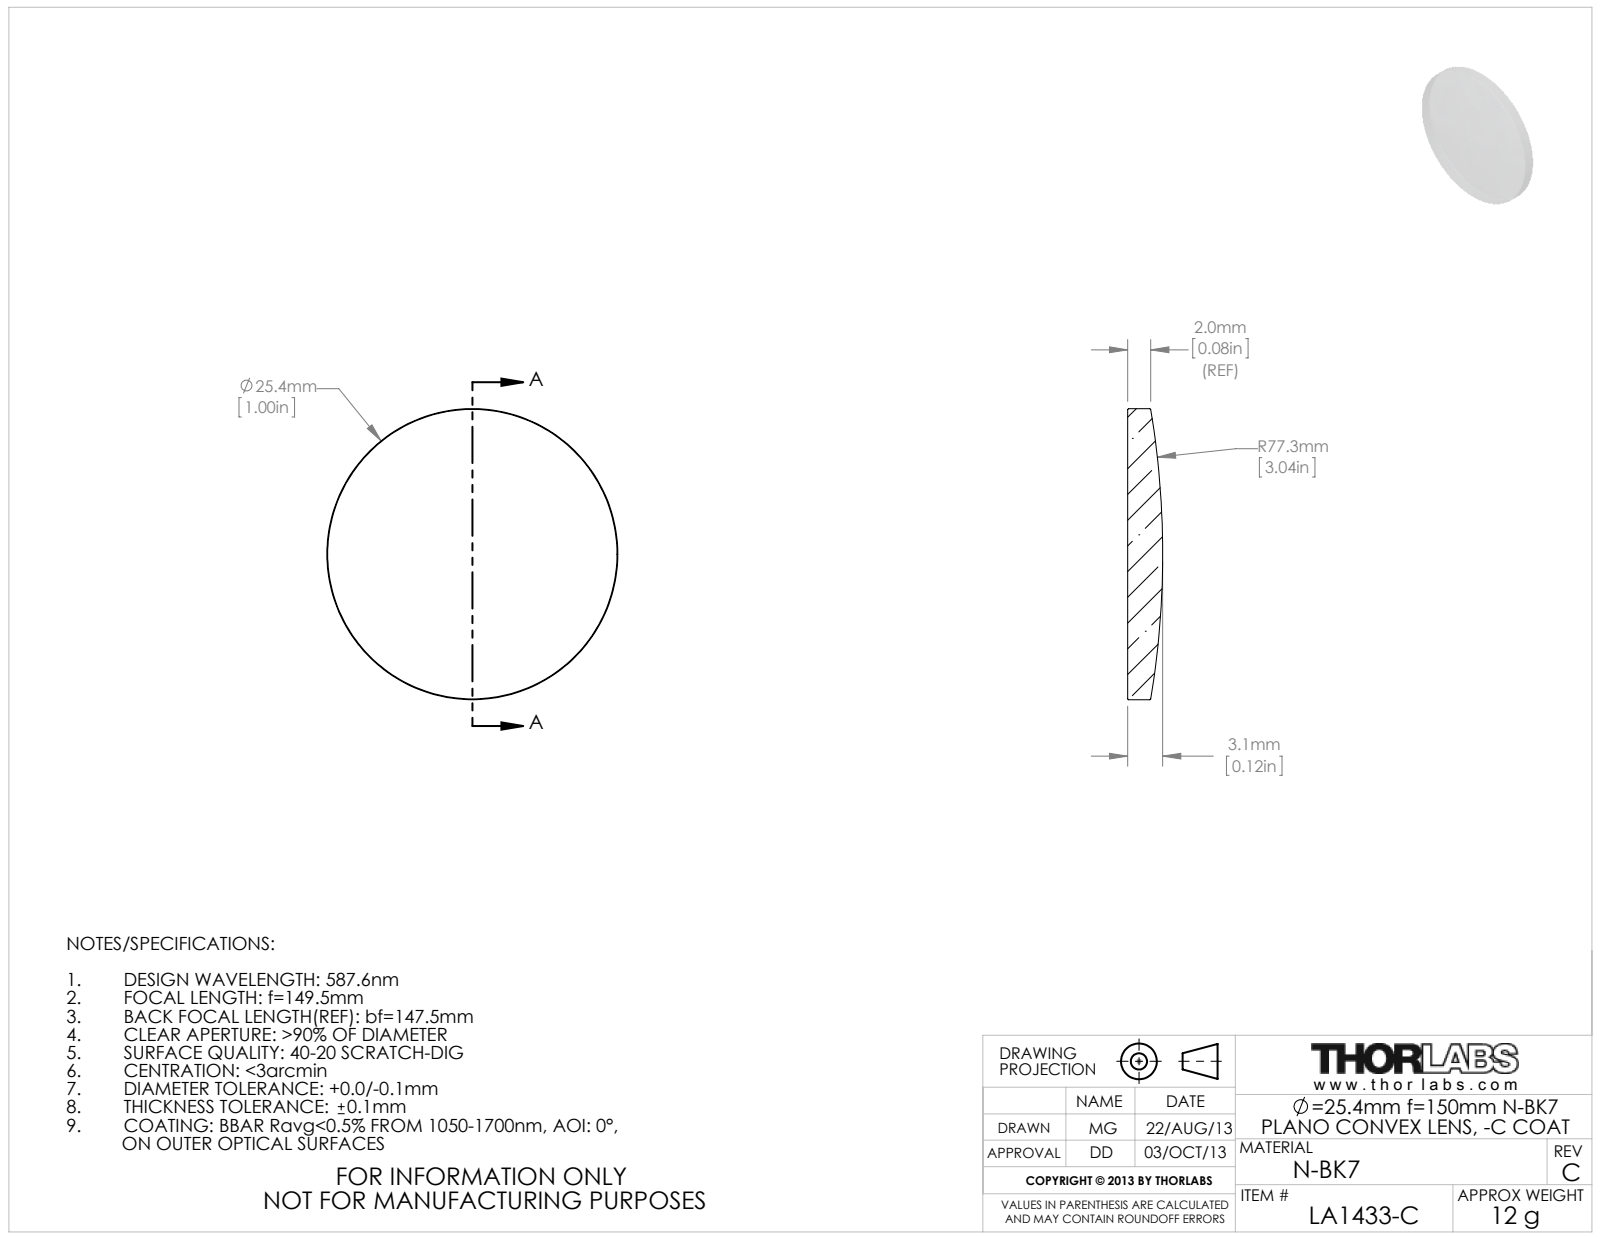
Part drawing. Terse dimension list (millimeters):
name: 4586-E0W
written by: SolidWorks 2009 (AUTOMOTIVE_DESIGN)
unit: mm
bodies: 1 solid, 5 faces (1 planar, 2 cylindrical, 2 other)
size: 25.4 × 25.4 × 3.05
volume: 1 280 mm³; area: 1 176 mm²
bosses: 1× ⌀25.4
